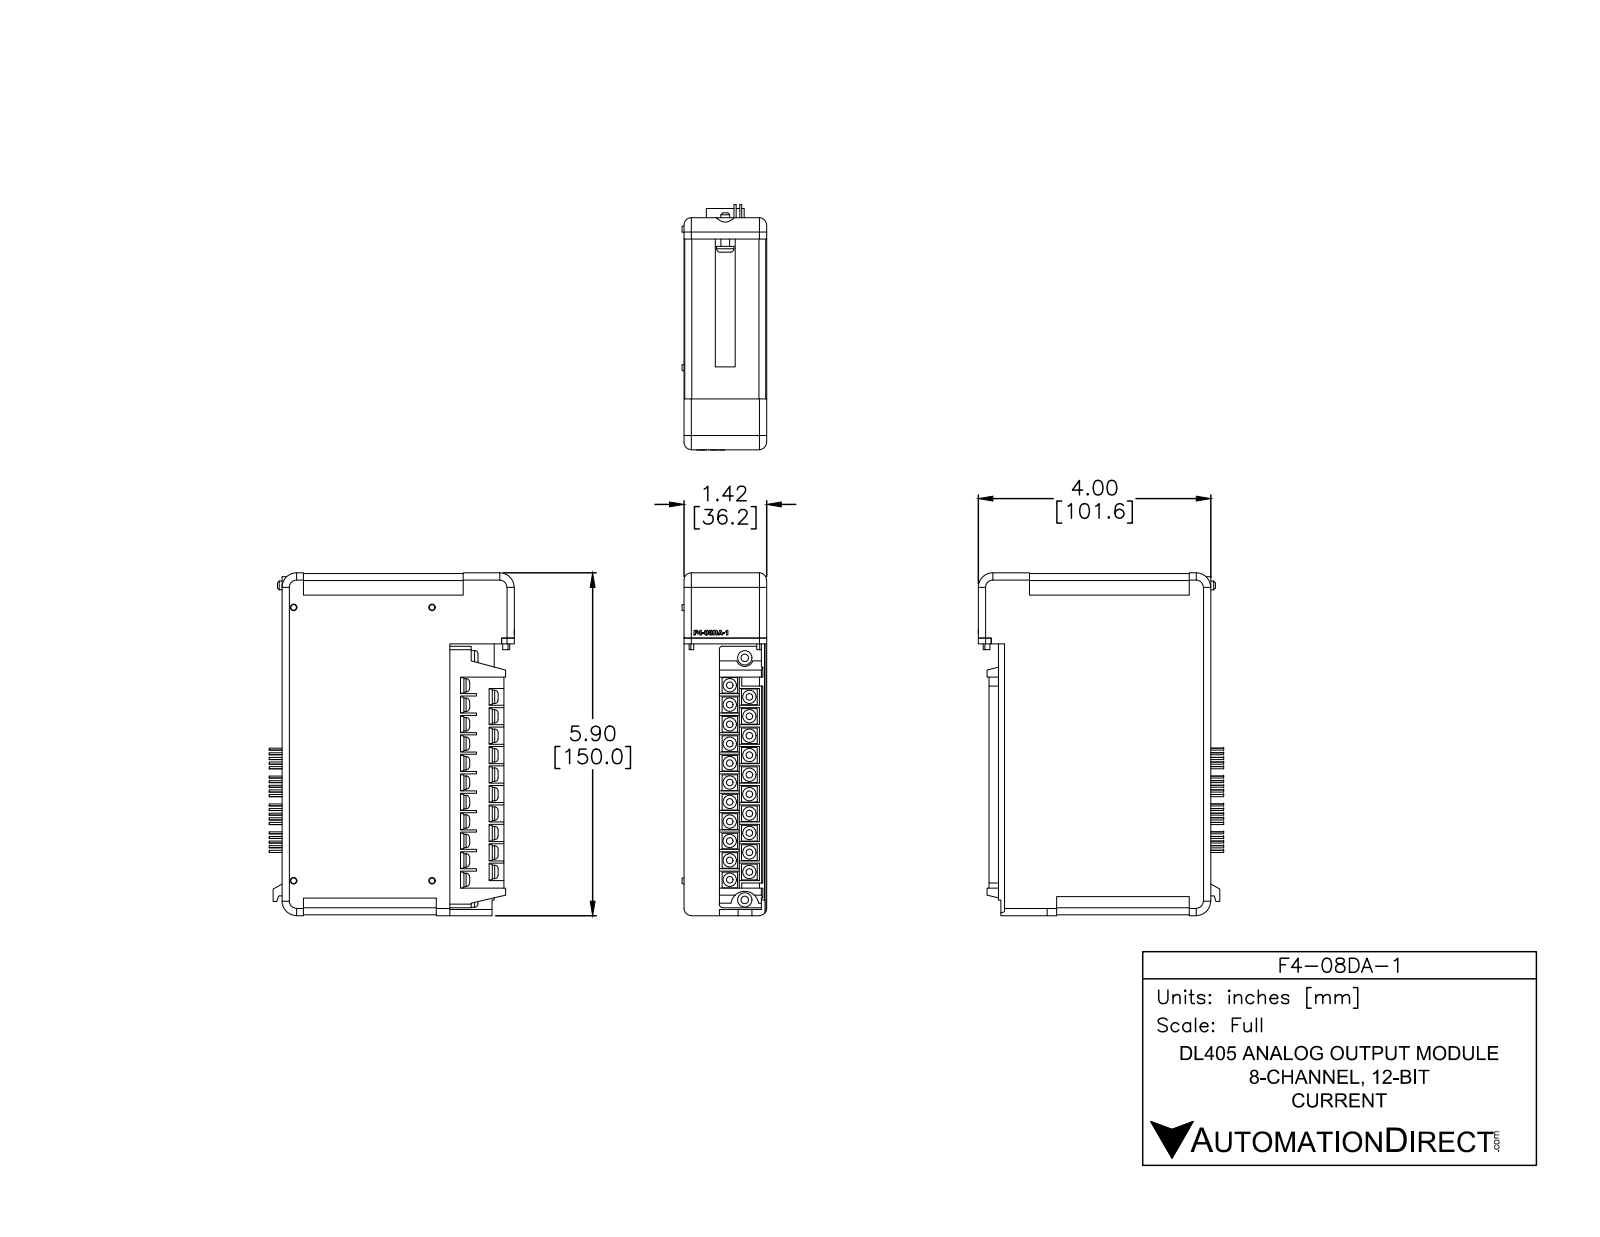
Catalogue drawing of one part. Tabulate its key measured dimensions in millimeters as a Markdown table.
| quantity | value |
| --- | --- |
| part name | F4-08DA-1 |
| STEP written by | SolidWorks 2014 (AUTOMOTIVE_DESIGN) |
| units | millimeters |
| bodies | 6 solids, 897 faces (556 planar, 246 cylindrical, 95 other) |
| overall size | 150 × 107.3 × 37 |
| volume | 452 300 mm³ |
| surface area | 58 370 mm² |
| round bosses / shafts (diameter × count) | 5.8 × 21, 0.9 × 20, 0.9 × 20, 6.4 × 2, 7.6 × 1, 3.8 × 1 |
| partial cylindrical surfaces (radius × count) | 0.4 × 82, 3.2 × 8, 3 × 4, 6.4 × 3, 0.8 × 2, 1.5 × 2, 3.8 × 1, 3.8 × 1 |
| main face-to-face distances | 36.2, 0.4, 73.4, 149.2, 35.8, 11.9, 24.3, 149.6, 30.7, 8.8 |
